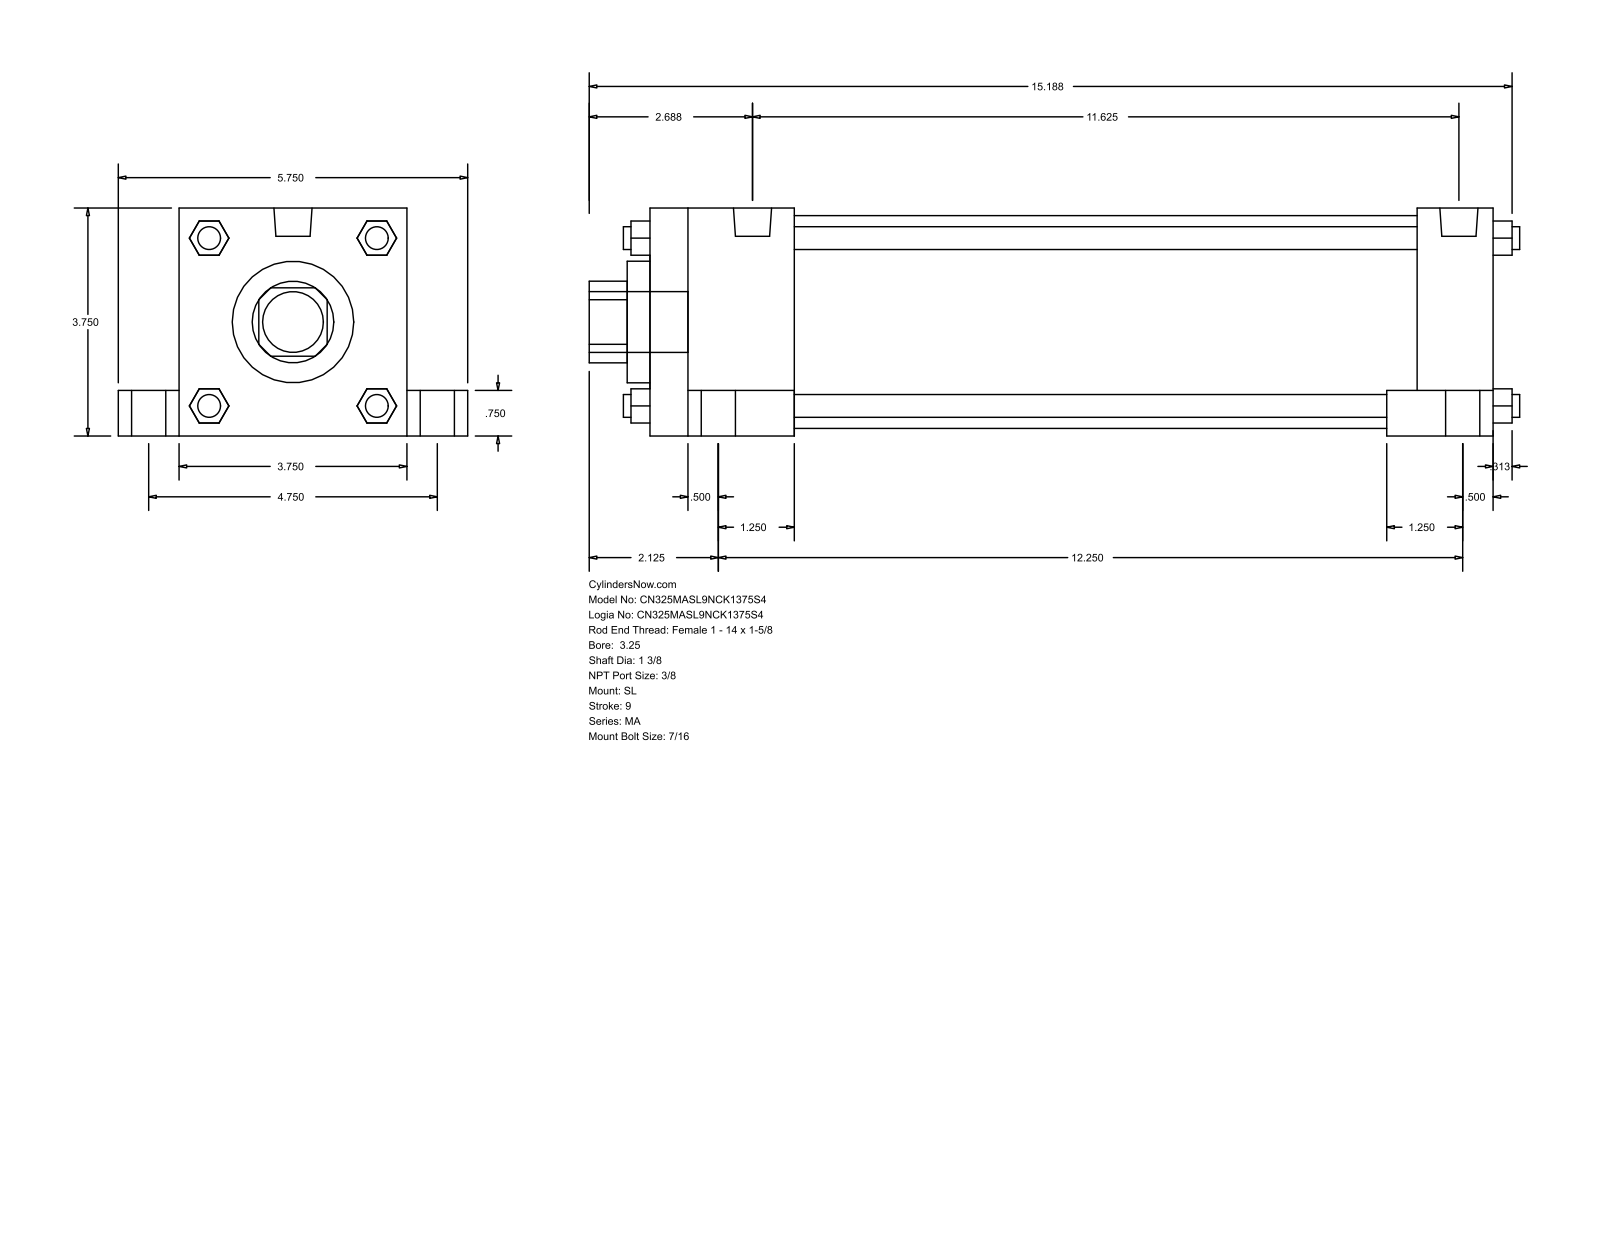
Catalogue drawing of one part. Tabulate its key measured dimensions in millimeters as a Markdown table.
| quantity | value |
| --- | --- |
| part name | MA_SL__0325_1.375 |
| STEP written by | GSSL Pune (CONFIG_CONTROL_DESIGN) |
| units | millimeters |
| bodies | 0 solids, 148 faces (112 planar, 36 cylindrical, 0 other) |
| overall size | 388.94 × 146.05 × 95.25 |
| round holes (diameter × count) | 34.92 × 1, 50.8 × 1, 88.9 × 1 |
| round bosses / shafts (diameter × count) | 20.64 × 4, 14.29 × 4, 11.11 × 4, 9.53 × 4, 15.93 × 2, 25.4 × 1 |
| partial cylindrical surfaces (radius × count) | 17.06 × 1 |
| main face-to-face distances | 95.24, 352.42, 260.35, 25.41, 120.65, 320.67, 31.75, 60.32, 292.1, 19.05 |
